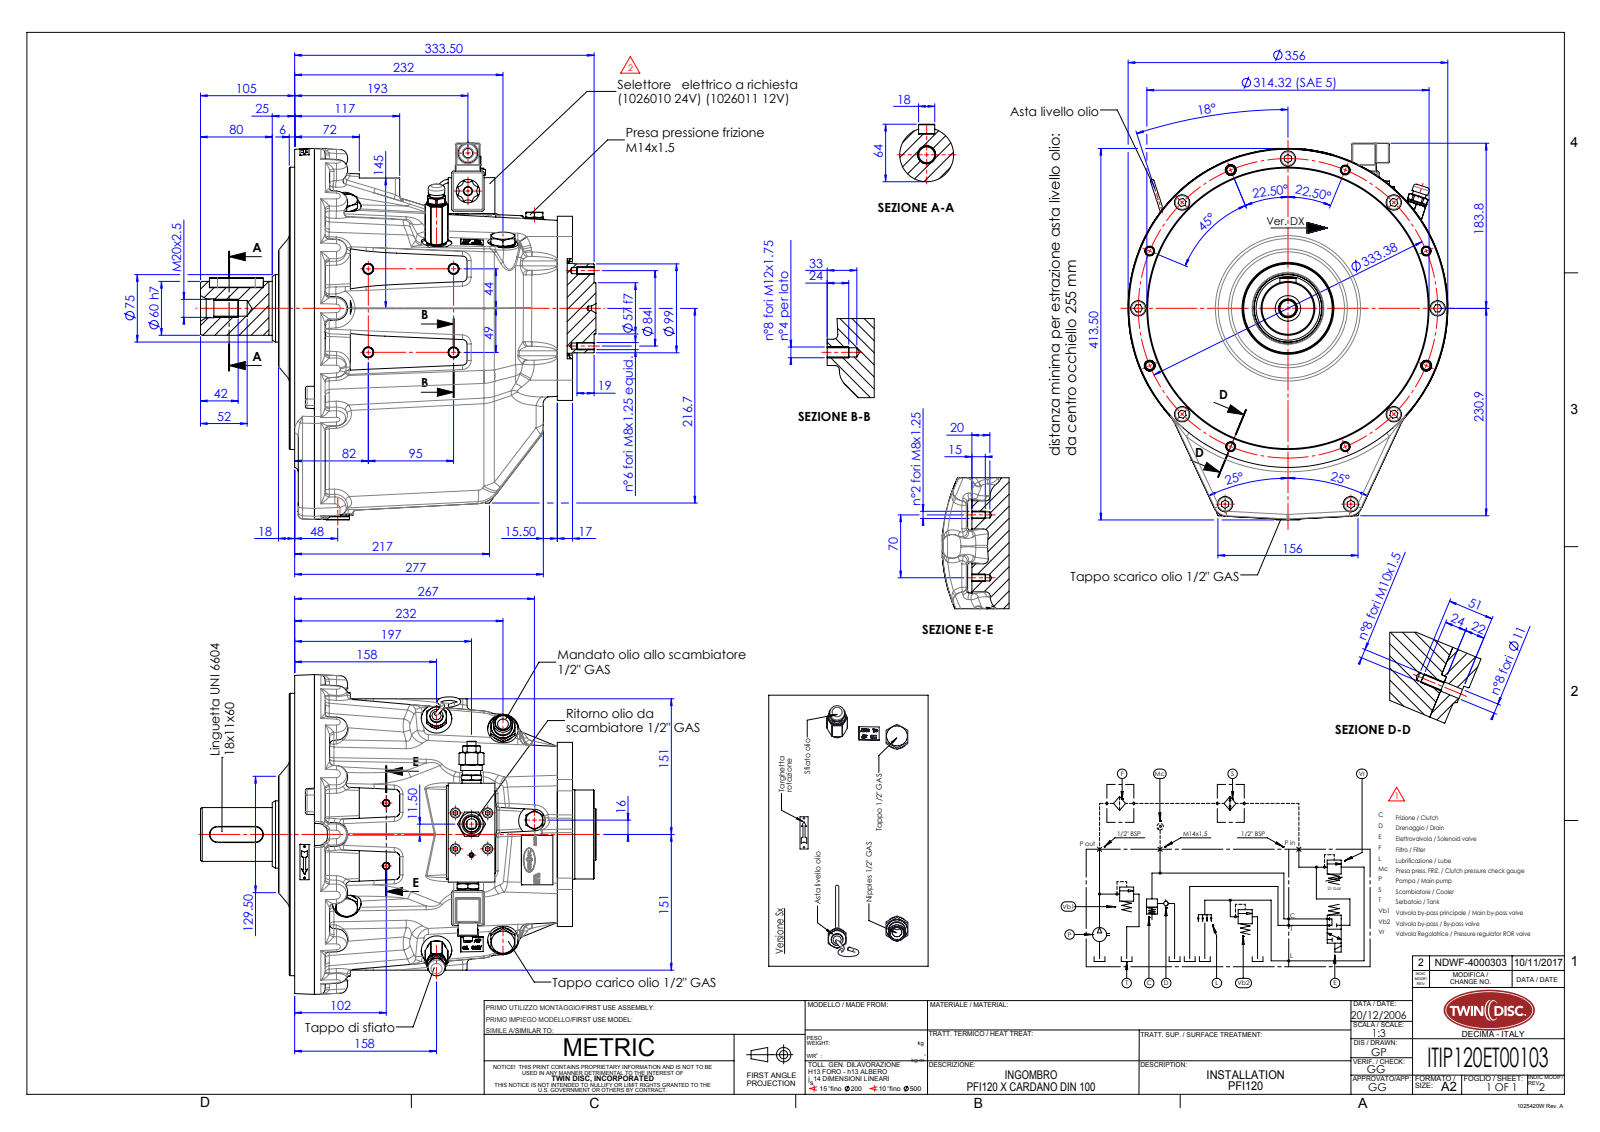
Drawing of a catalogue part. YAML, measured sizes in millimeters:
part_name: "ITIP120ET00103"
step_written_by: "SolidWorks 2015 (AUTOMOTIVE_DESIGN)"
units: millimeters
bodies: {solids: 0, faces: 1671, planar: 497, cylindrical: 404, other: 770}
overall_size: [440.4, 419.35, 356]
round_holes:
  - {diameter: 11, count: 12}
  - {diameter: 17, count: 9}
  - {diameter: 6.8, count: 8}
  - {diameter: 10.2, count: 4}
  - {diameter: 34, count: 4}
  - {diameter: 10, count: 2}
  - {diameter: 12, count: 2}
  - {diameter: 2, count: 1}
  - {diameter: 5, count: 1}
  - {diameter: 10.5, count: 1}
  - {diameter: 17.5, count: 1}
  - {diameter: 21, count: 1}
round_bosses_or_shafts:
  - {diameter: 36, count: 4}
  - {diameter: 27, count: 3}
  - {diameter: 22, count: 3}
  - {diameter: 4, count: 3}
  - {diameter: 26.18, count: 2}
  - {diameter: 20.95, count: 2}
  - {diameter: 20, count: 2}
  - {diameter: 16, count: 2}
partial_cylinders:
  - {radius: 5, count: 89}
  - {radius: 1, count: 36}
  - {radius: 22, count: 26}
  - {radius: 2, count: 18}
  - {radius: 3, count: 16}
  - {radius: 28, count: 14}
  - {radius: 15, count: 11}
  - {radius: 10, count: 10}
face_to_face_distances: [28, 270.5, 298.5, 22, 17, 315.5, 287.5, 6, 309.5, 292.5]
hole_center_spacings: [166.69, 65.04, 127.58, 42, 185.22, 235.73, 277.2, 308]
